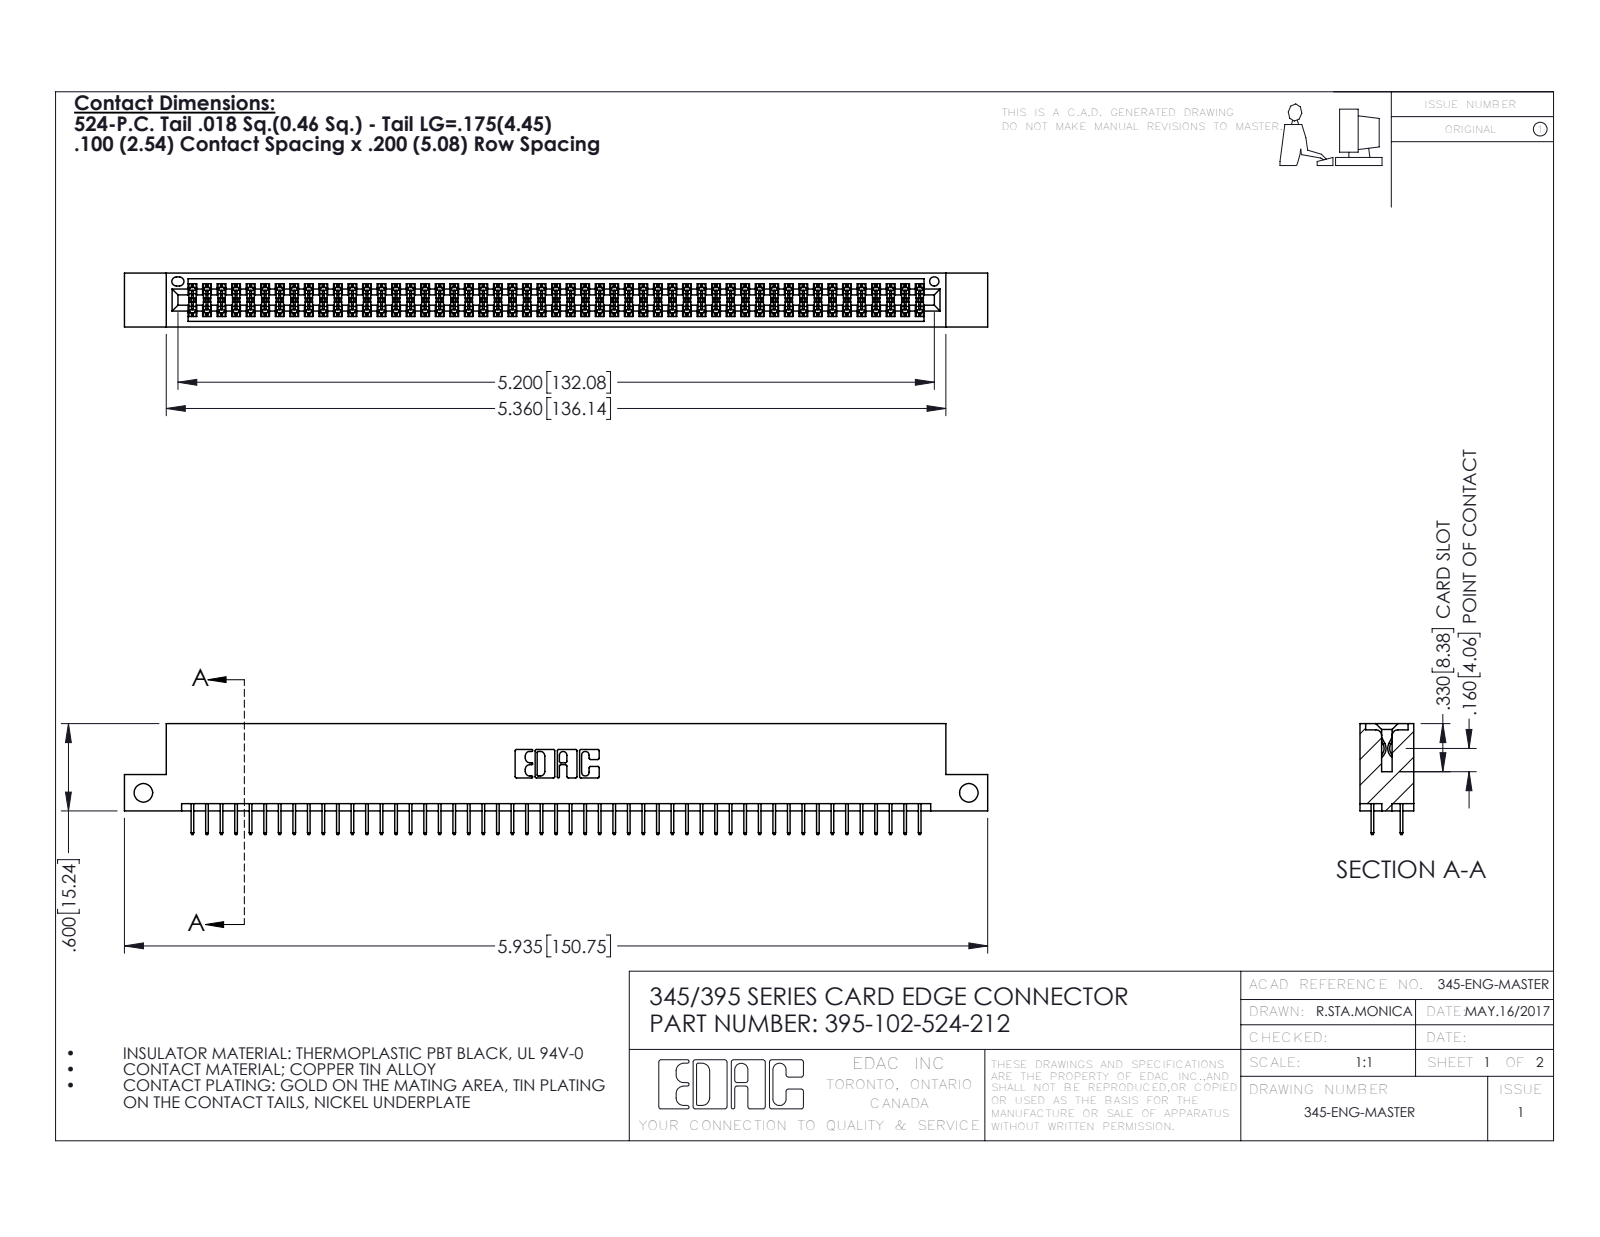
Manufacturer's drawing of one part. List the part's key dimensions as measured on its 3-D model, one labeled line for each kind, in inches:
Part name (STEP PRODUCT): 395-102-524-212; 345-292-001_345-293-124; 345 Part_Flush Mounting Lugs - Side Mount
STEP written by: SolidWorks 2016 (CONFIG_CONTROL_DESIGN)
Units: inches
Bodies: 103 solids, 5634 faces (4058 planar, 1576 cylindrical, 0 other)
Overall size (bounding box): 5.935 × 0.762 × 0.37
Volume: 0.884 in³ · Surface area: 32.62 in²
Round holes (diameter × count): ⌀0.128 ×2, ⌀0.064 ×1
Partial cylindrical surfaces — rounded edges, fillets, slot ends (radius × count): R0.006 ×153, R0.01 ×22, R0.007 ×6, R0.031 ×6, R0.026 ×3, R0.014 ×2, R0.019 ×2, R0.022 ×2
Main face-to-face distances: 0.298, 0.072, 0.2, 0.37, 0.098, 0.272, 0.025, 0.225, 0.072, 0.175
Hole centre spacings: 5.675
